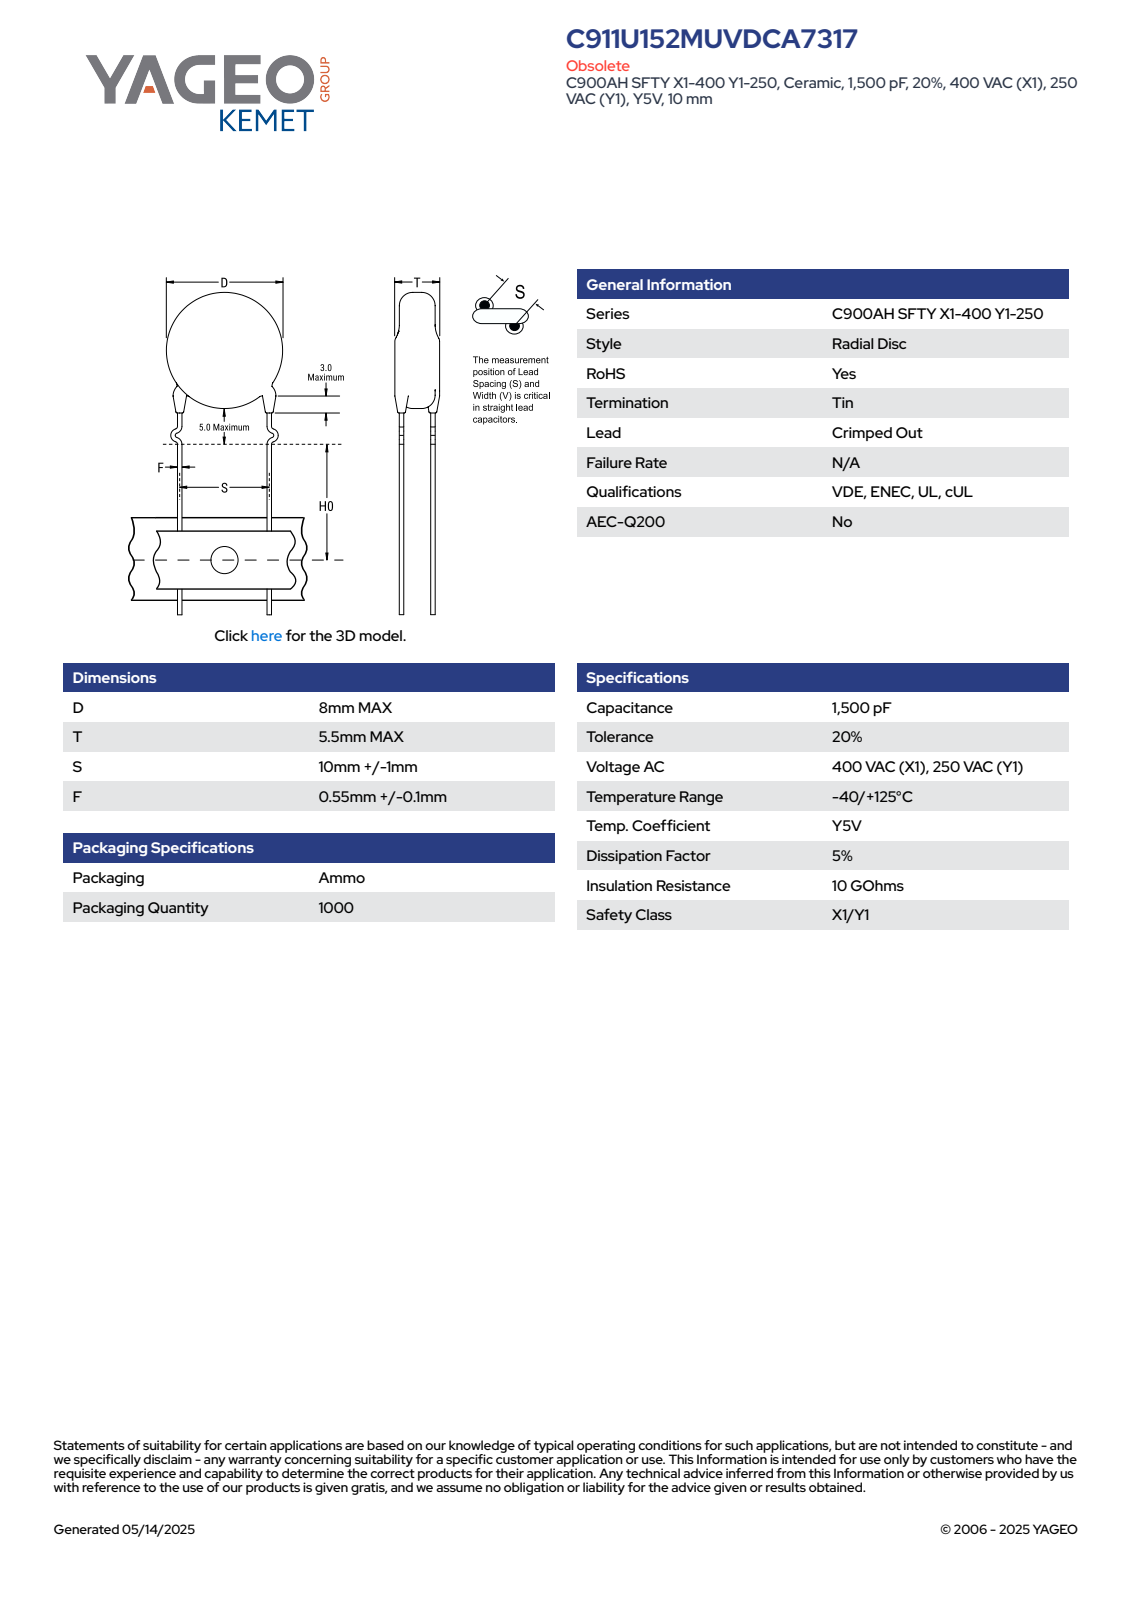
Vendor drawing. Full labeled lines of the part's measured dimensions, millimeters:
Part name (STEP PRODUCT): CCD_KCOC900_D8T5.5S10LL20F0.55
STEP written by: SolidWorks 2014 (AUTOMOTIVE_DESIGN)
Units: millimetres
Bodies: 4 solids, 93 faces (63 planar, 10 cylindrical, 20 other)
Overall size (bounding box): 33 × 13.98 × 6.72
Volume: 291 mm³ · Surface area: 356 mm²
Round bosses / shafts (diameter × count): ⌀1.2 ×4, ⌀8 ×1
Main face-to-face distances: 5.5, 0.83, 4.42, 3.59, 3.39, 0.52, 0.31, 0.67, 1.71, 2.46
